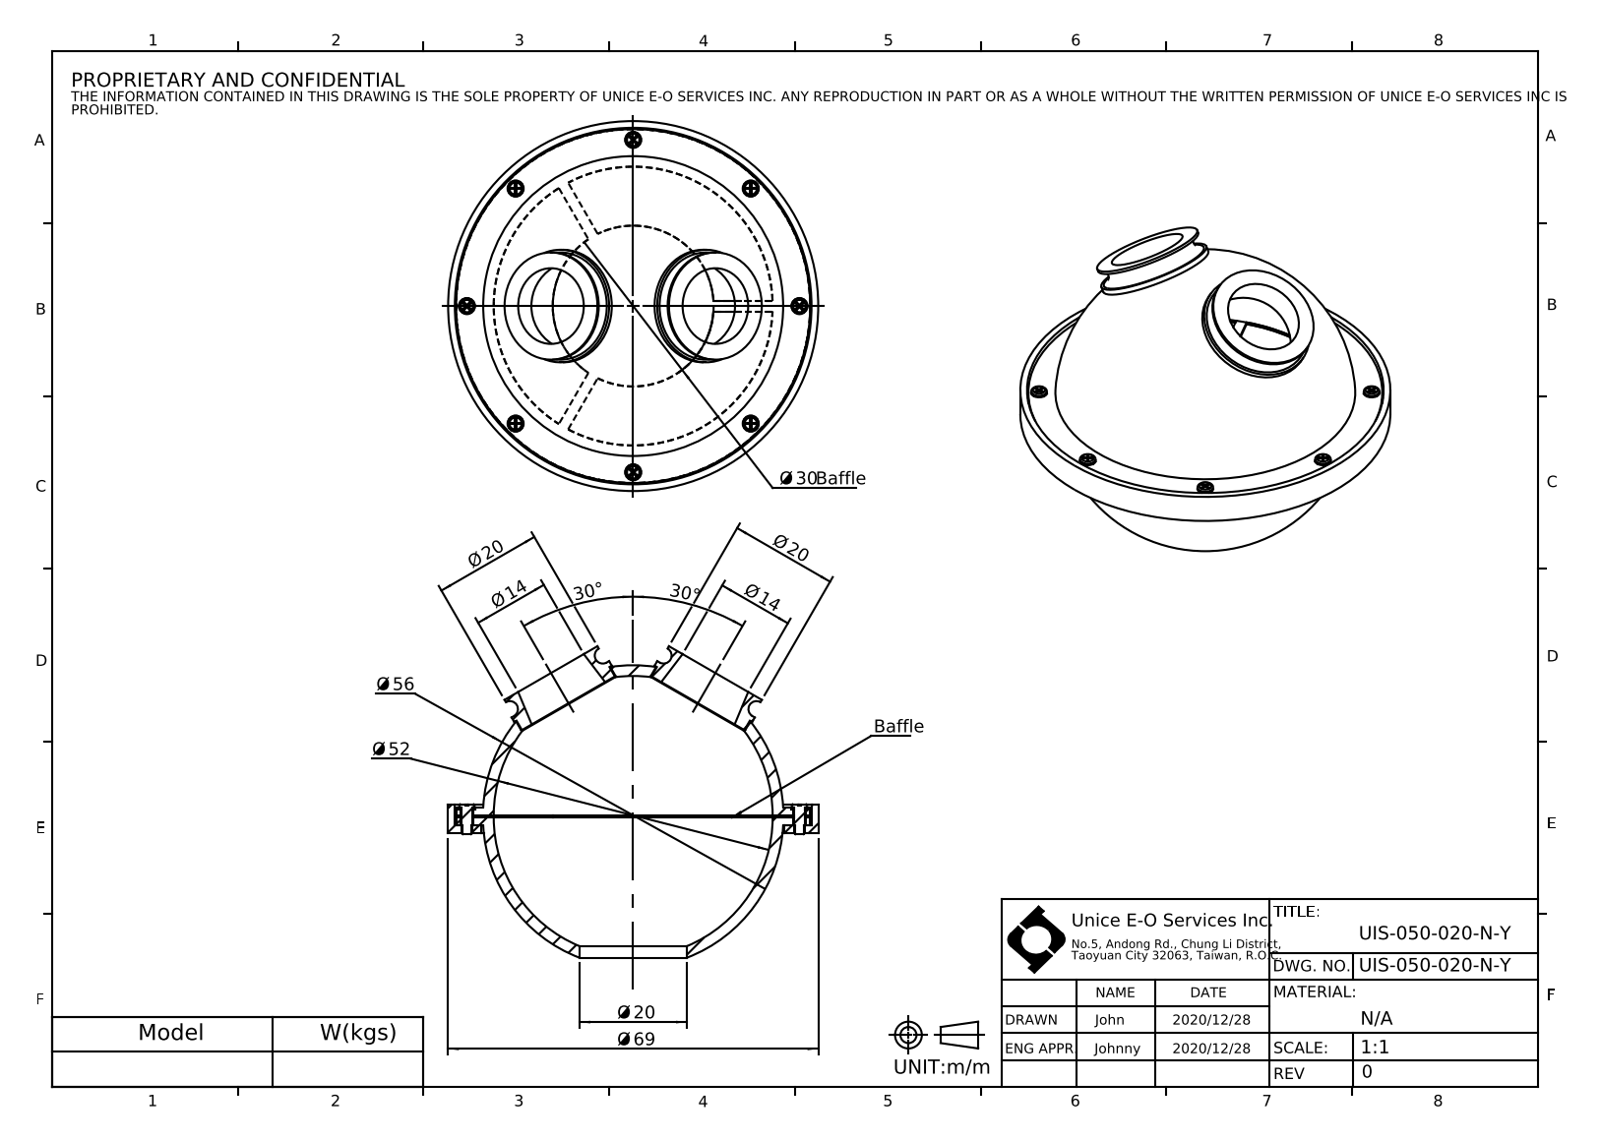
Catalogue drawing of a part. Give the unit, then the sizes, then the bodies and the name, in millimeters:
Units: millimetres
Overall size (bounding box): 69 × 69 × 58.1
Round holes (diameter × count): ⌀3 ×4, ⌀20 ×1, ⌀52 ×1, ⌀56.5 ×1, ⌀66.5 ×1
Round bosses / shafts (diameter × count): ⌀1.9 ×8, ⌀21 ×2, ⌀20.3 ×2, ⌀20 ×2, ⌀69 ×1, ⌀66 ×1
Main face-to-face distances: 1.5, 3.4, 1.9, 0.4, 3, 4.9, 5.5, 4, 2.5, 2.1
Hole centre spacings: 31, 43.84, 62
Bodies: 0 solids, 195 faces (78 planar, 49 cylindrical, 68 other)
Part name (STEP PRODUCT): UIS-050-020-N-Y
STEP written by: SolidWorks 2020 (CONFIG_CONTROL_DESIGN)
